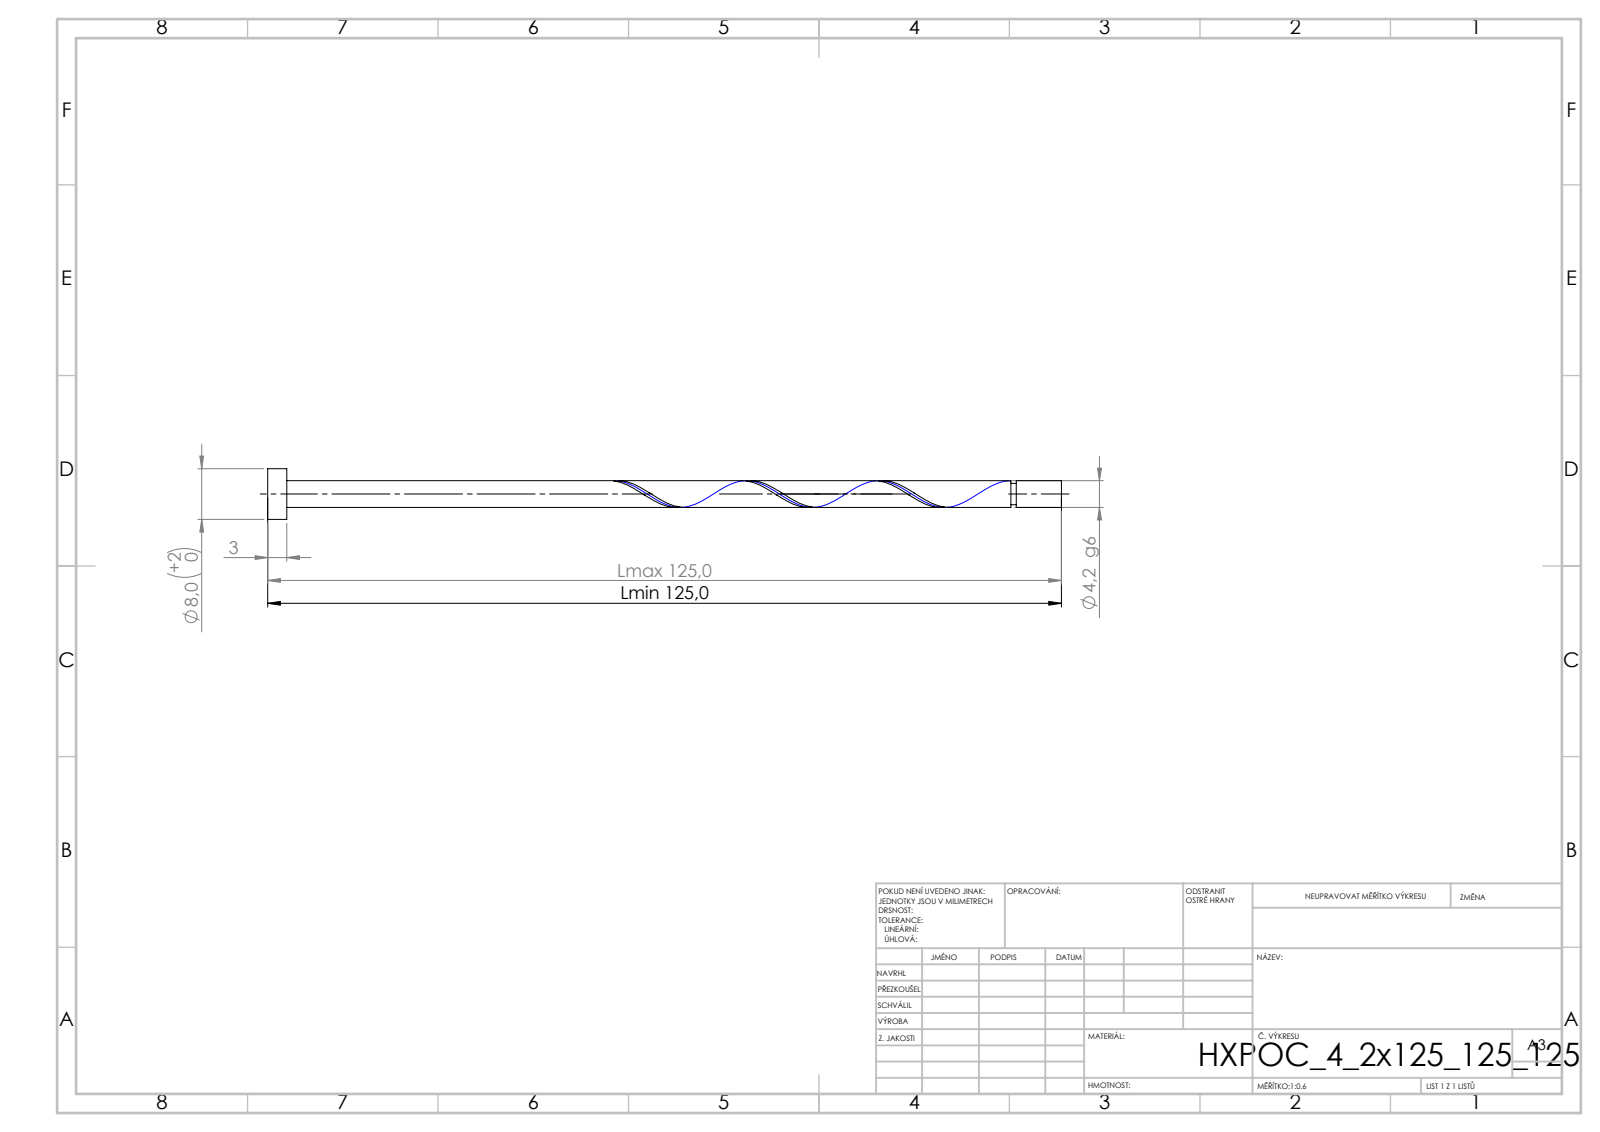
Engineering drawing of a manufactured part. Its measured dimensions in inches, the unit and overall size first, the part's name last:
Units: inches
Overall size (bounding box): 4.921 × 0.315 × 0.315
Round bosses / shafts (diameter × count): ⌀0.315 ×1, ⌀0.165 ×1, ⌀0.132 ×1
Main face-to-face distances: 0.118, 4.921, 4.803, 4.641, 4.523, 0.28, 4.608, 4.49, 0.033, 0.313
Volume: 0.111 in³ · Surface area: 2.829 in²
Bodies: 1 solid, 21 faces (6 planar, 14 cylindrical, 1 other)
STEP written by: SolidWorks 2019 (CONFIG_CONTROL_DESIGN)
